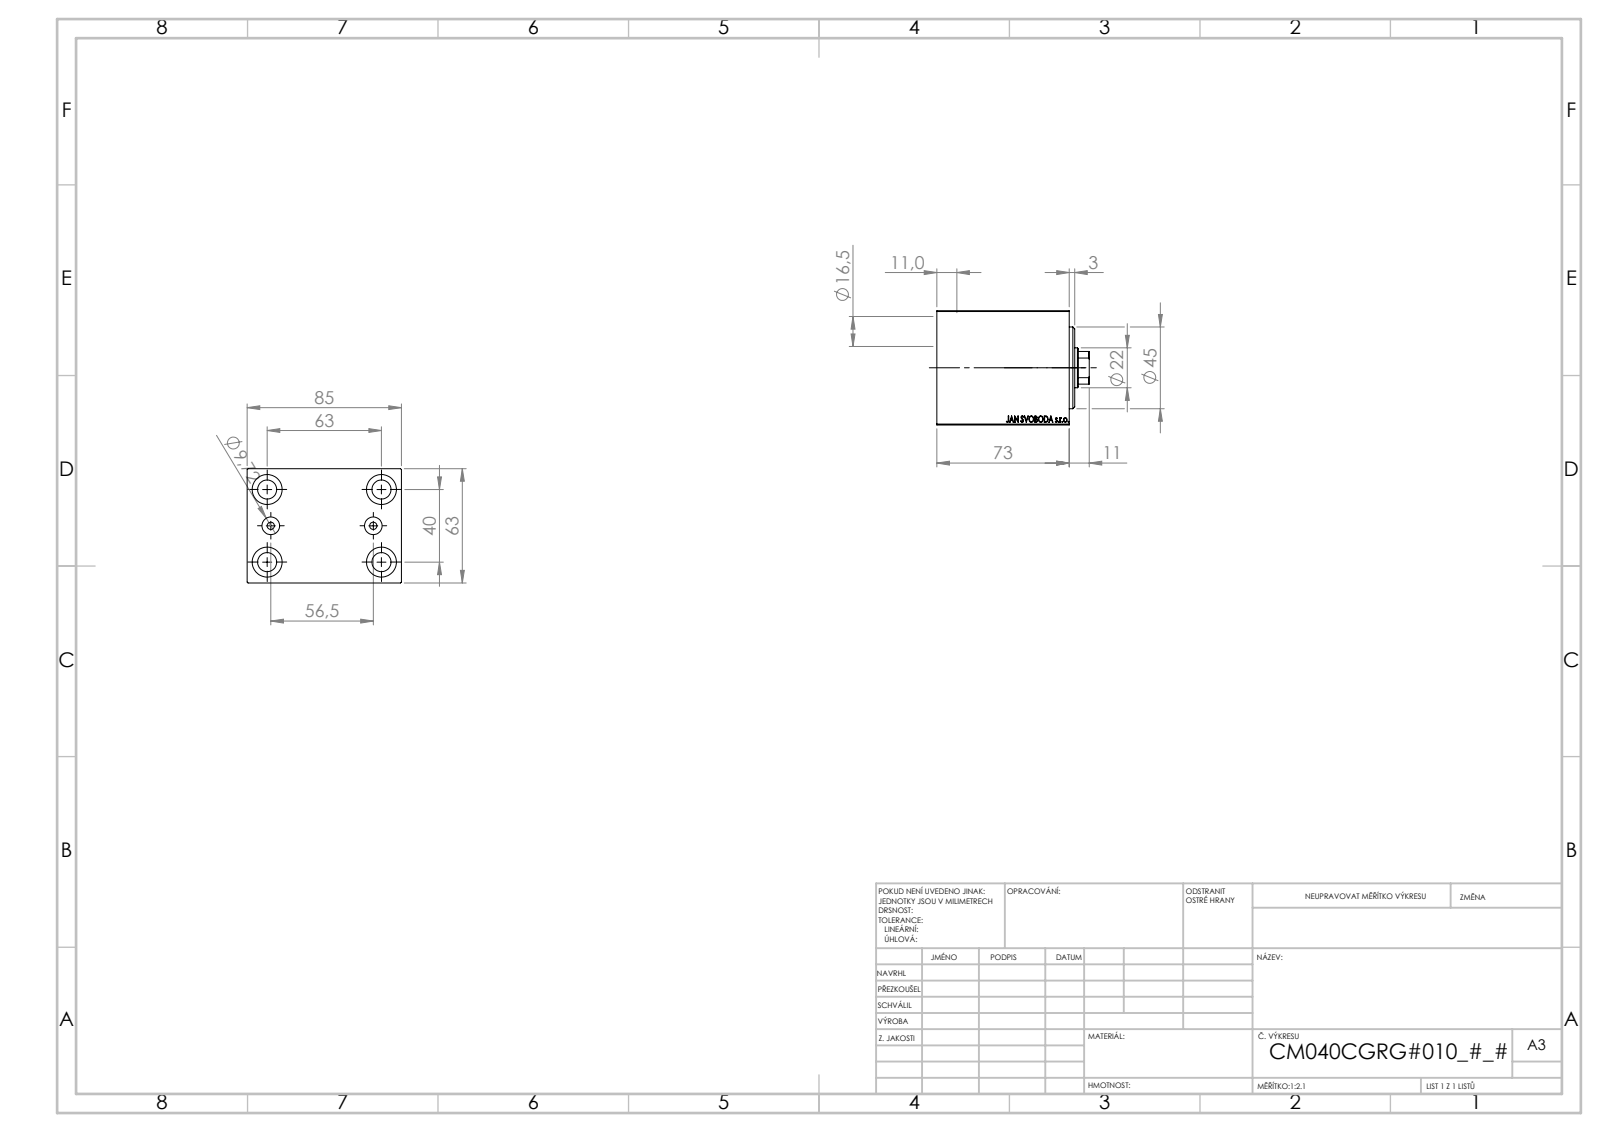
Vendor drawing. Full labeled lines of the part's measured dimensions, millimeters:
Part name (STEP PRODUCT): V450CM_VC_B; V450CM_C_VCP; V450CM_C_Body
STEP written by: SolidWorks 2019 (CONFIG_CONTROL_DESIGN)
Units: millimetres
Bodies: 3 solids, 858 faces (408 planar, 56 cylindrical, 394 other)
Overall size (bounding box): 85 × 85 × 63
Volume: 347 561 mm³ · Surface area: 62 334 mm²
Round holes (diameter × count): ⌀10.5 ×4, ⌀16.5 ×4, ⌀4 ×2, ⌀9.72 ×2, ⌀12.5 ×1, ⌀22 ×1, ⌀25.5 ×1, ⌀40 ×1, ⌀42 ×1, ⌀45 ×1
Partial cylindrical surfaces — rounded edges, fillets, slot ends (radius × count): R10.5 ×1
Main face-to-face distances: 63, 85, 73, 37, 36, 10, 27, 17, 11, 23
Hole centre spacings: 20.26, 37.31, 63.01, 28.25, 40, 63, 74.63, 56.5
